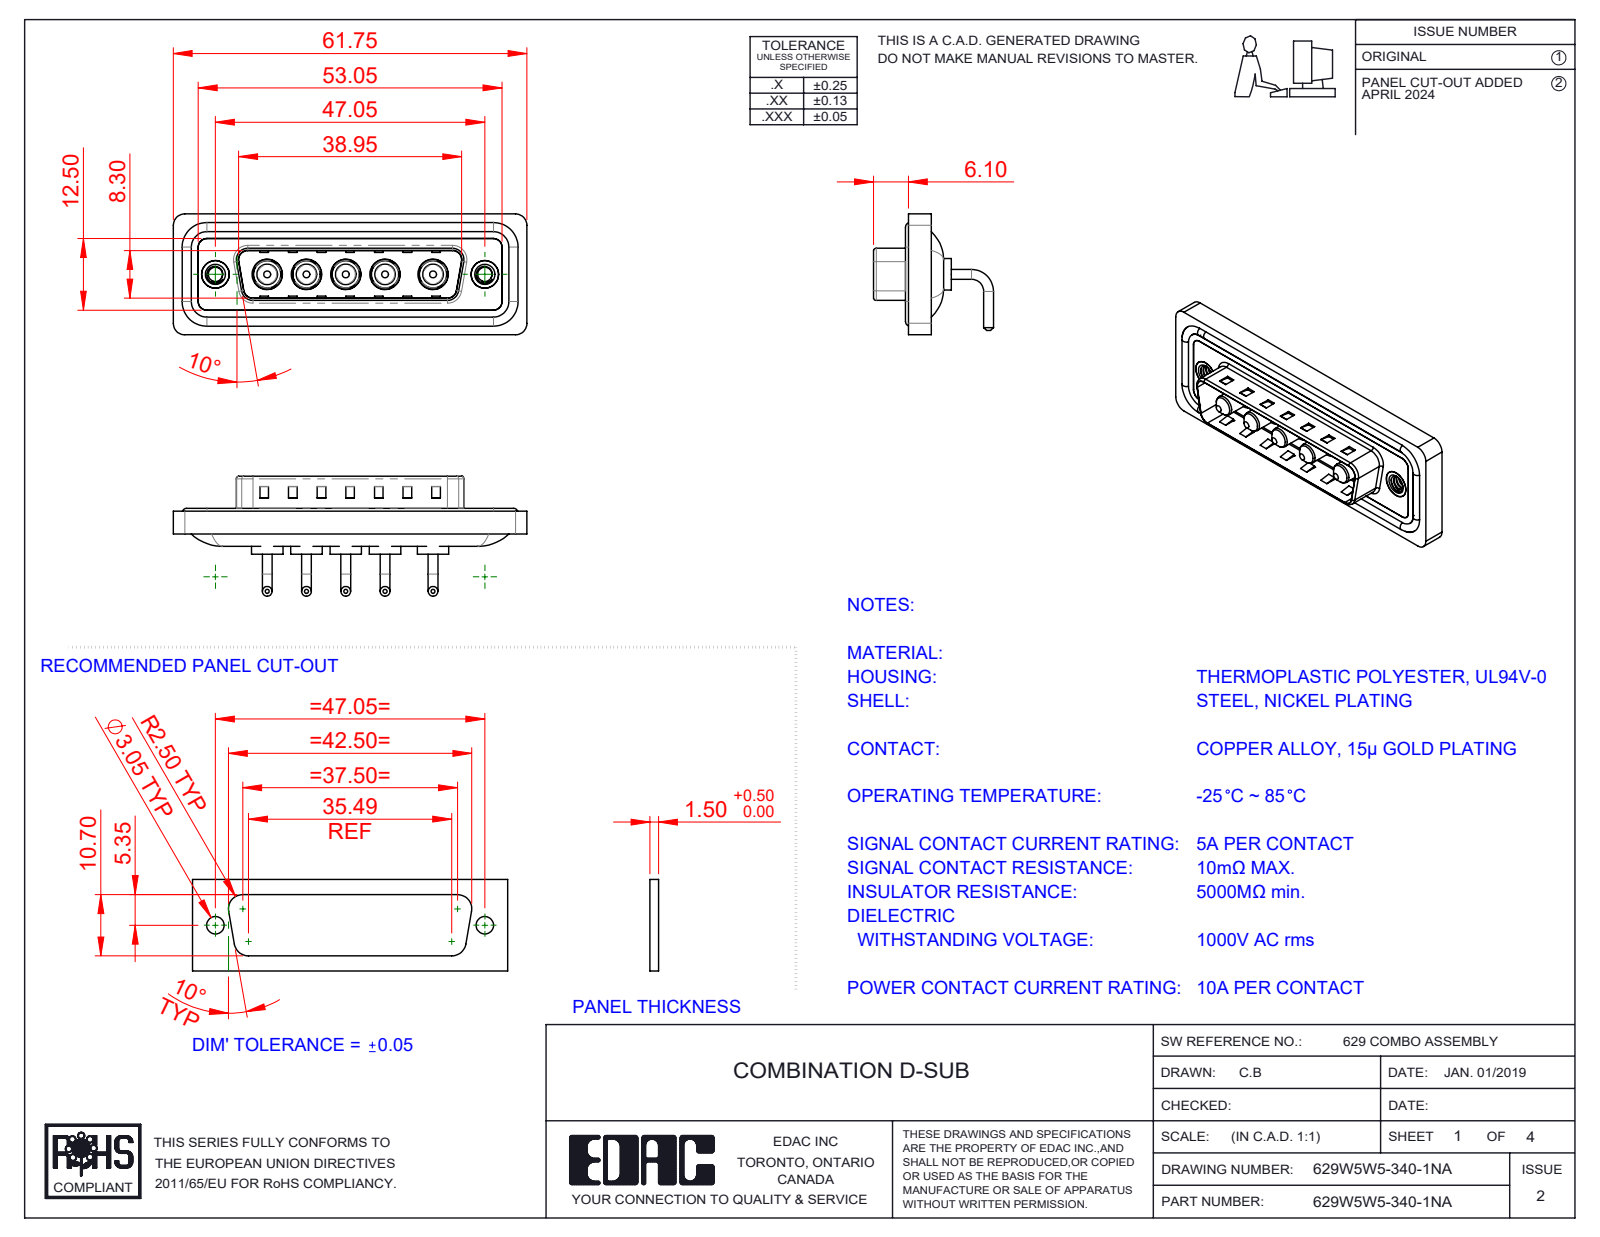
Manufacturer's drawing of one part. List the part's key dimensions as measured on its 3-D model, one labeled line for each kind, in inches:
Part name (STEP PRODUCT): 629Combo Threaded Rivet_A; 629Combo Shell Rear_25 Contacts; 629Combo Waterproof Housing_25 Contacts; Power Pin_10A RA (+3 more)
STEP written by: SolidWorks 2023 (CONFIG_CONTROL_DESIGN)
Units: inches
Bodies: 17 solids, 692 faces (259 planar, 291 cylindrical, 142 other)
Overall size (bounding box): 2.431 × 0.831 × 0.825
Volume: 0.459 in³ · Surface area: 18.63 in²
Round holes (diameter × count): ⌀0.191 ×5, ⌀0.209 ×5, ⌀0.098 ×2, ⌀0.157 ×2, ⌀0.189 ×2, ⌀0.197 ×2
Round bosses / shafts (diameter × count): ⌀0.067 ×10, ⌀0.217 ×5, ⌀0.205 ×5, ⌀0.187 ×5, ⌀0.148 ×5, ⌀0.142 ×5, ⌀0.063 ×4, ⌀0.193 ×2
Partial cylindrical surfaces — rounded edges, fillets, slot ends (radius × count): R0.059 ×18, R0.079 ×18, R0.02 ×8, R0.063 ×8, R0.083 ×5, R0.01 ×4, R0.024 ×4, R0.026 ×4
Main face-to-face distances: 0.016, 0.114, 0.031, 0.177, 0.161, 0.059, 0.043, 0.083, 0.122, 0.236
Hole centre spacings: 0.27, 0.541, 0.27, 0.27, 0.33, 0.33, 0.356, 0.356
